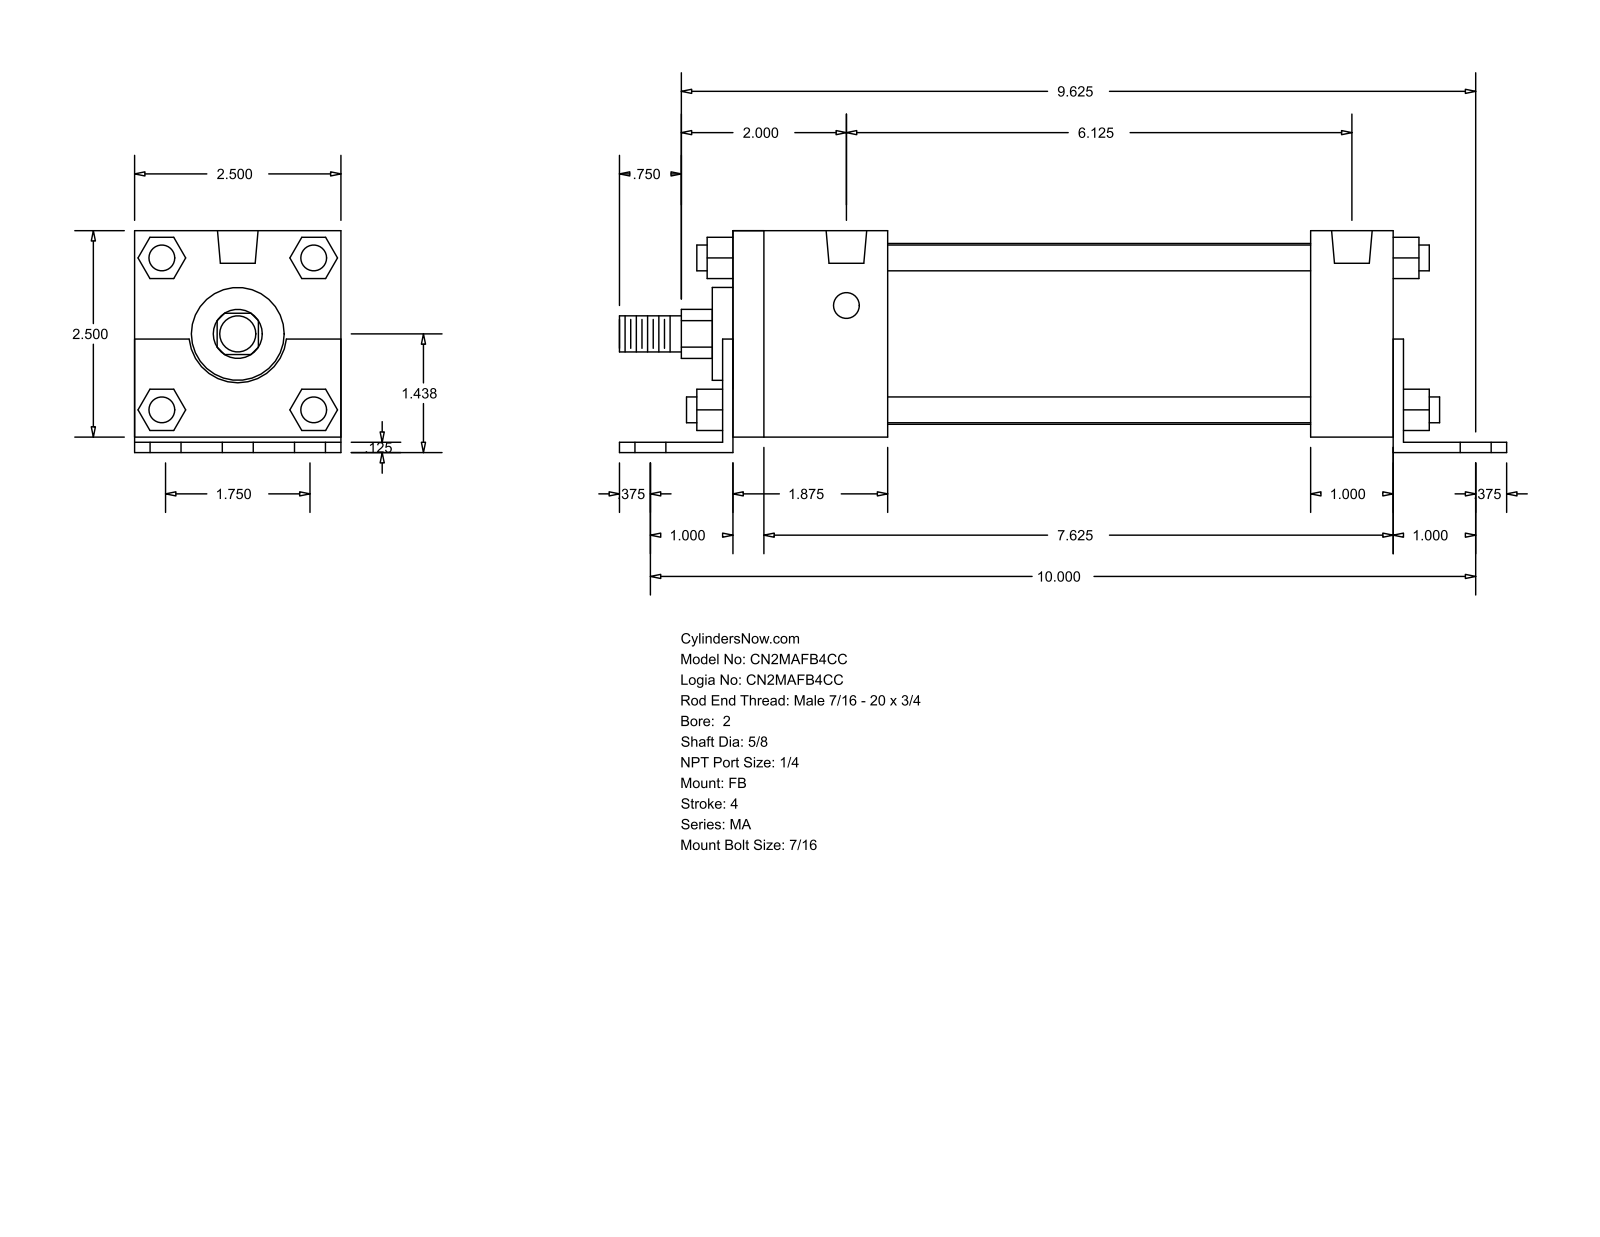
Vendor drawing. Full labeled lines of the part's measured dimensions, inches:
Part name (STEP PRODUCT): MA_FB__0200_0.625
STEP written by: GSSL Pune (CONFIG_CONTROL_DESIGN)
Units: inches
Bodies: 0 solids, 140 faces (105 planar, 35 cylindrical, 0 other)
Overall size (bounding box): 10.75 × 2.687 × 2.5
Round holes (diameter × count): ⌀0.437 ×6, ⌀0.313 ×4, ⌀0.492 ×2
Round bosses / shafts (diameter × count): ⌀0.313 ×4, ⌀2.19 ×1, ⌀1.125 ×1, ⌀0.625 ×1, ⌀0.437 ×1
Partial cylindrical surfaces — rounded edges, fillets, slot ends (radius × count): R0.297 ×1, R0.593 ×1
Main face-to-face distances: 2.5, 0.187, 0.125, 2.687, 0.063, 0.125, 2.563, 8.125, 8, 0.5
Hole centre spacings: 0.875, 10.038, 10, 1.736, 1.75, 2.531, 6.125, 7.675
